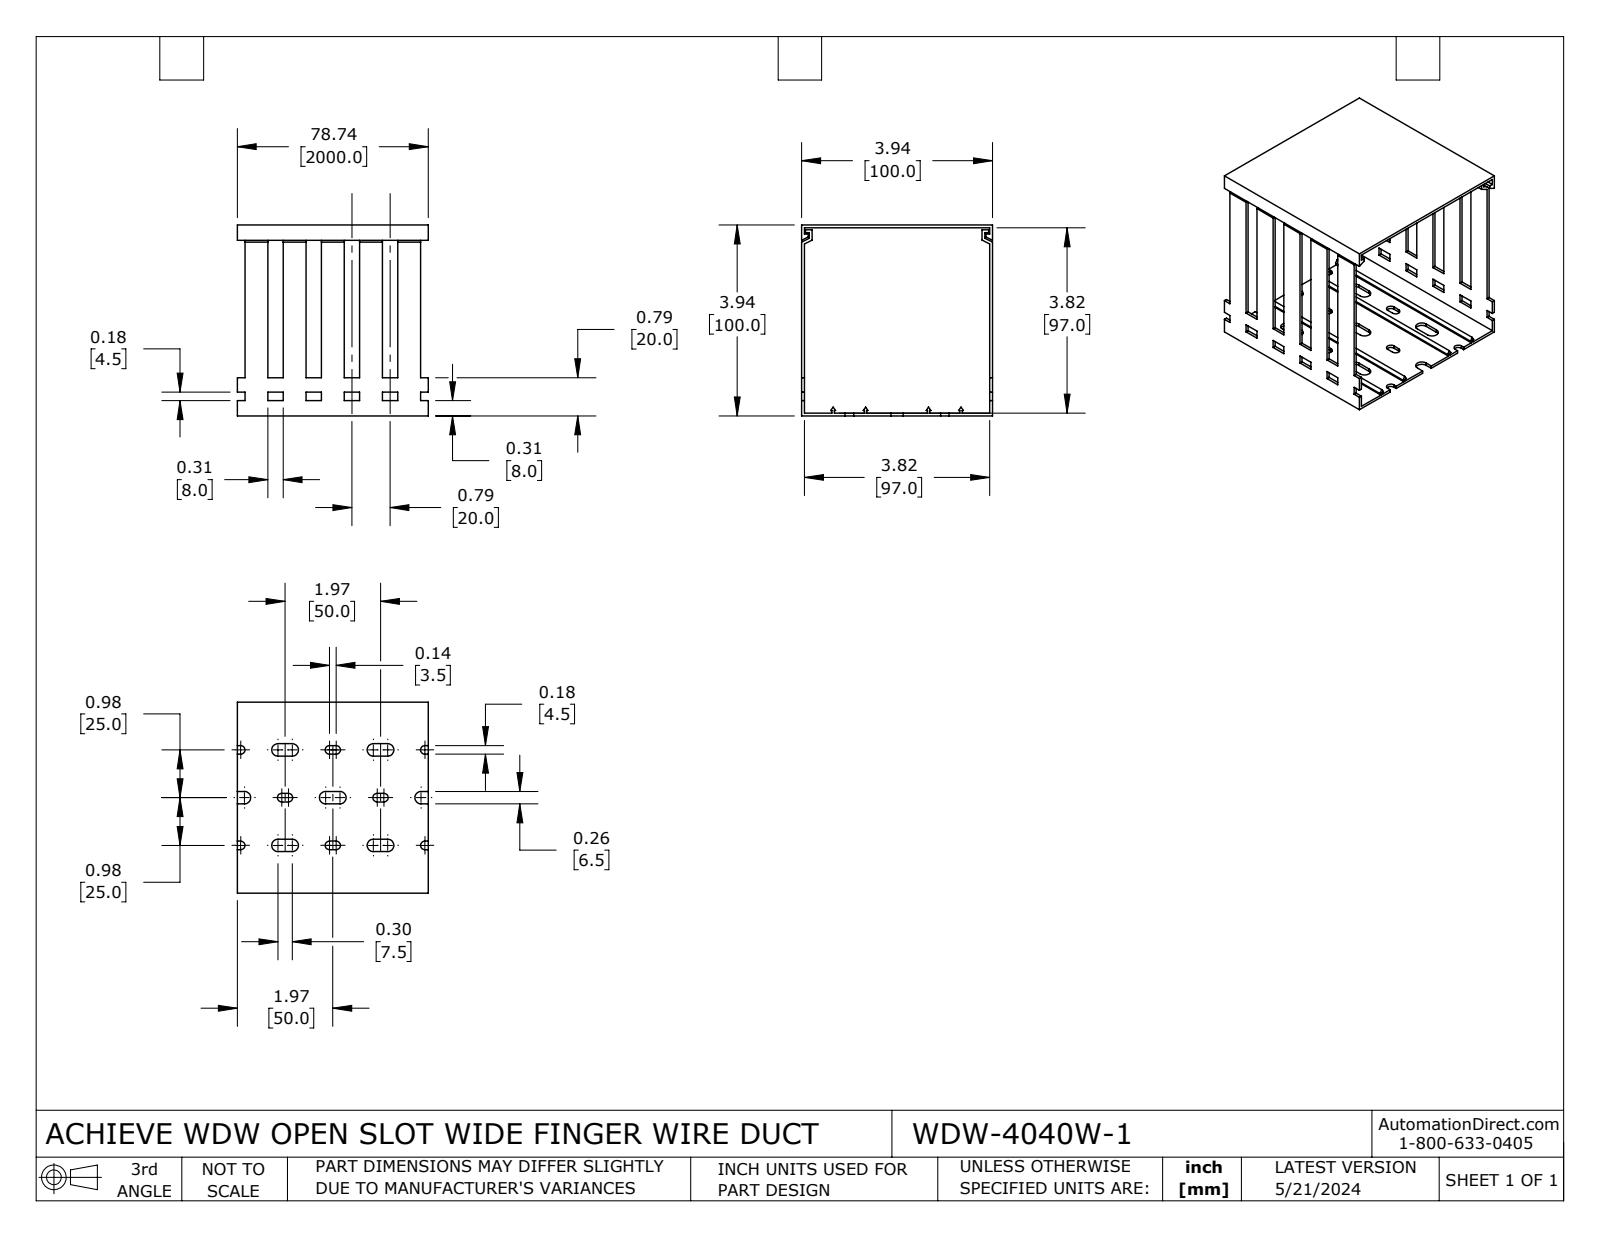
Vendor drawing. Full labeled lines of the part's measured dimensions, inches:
Part name (STEP PRODUCT): WDW-4040W-1
STEP written by: SolidWorks 2023 (CONFIG_CONTROL_DESIGN)
Units: inches
Bodies: 2 solids, 272 faces (236 planar, 36 cylindrical, 0 other)
Overall size (bounding box): 3.937 × 3.937 × 3.937
Volume: 3.229 in³ · Surface area: 117.3 in²
Partial cylindrical surfaces — rounded edges, fillets, slot ends (radius × count): R0.089 ×12, R0.128 ×12
Main face-to-face distances: 0.059, 3.878, 3.937, 3.819, 0.787, 0.157, 3.78, 1.575, 3.72, 0.472
